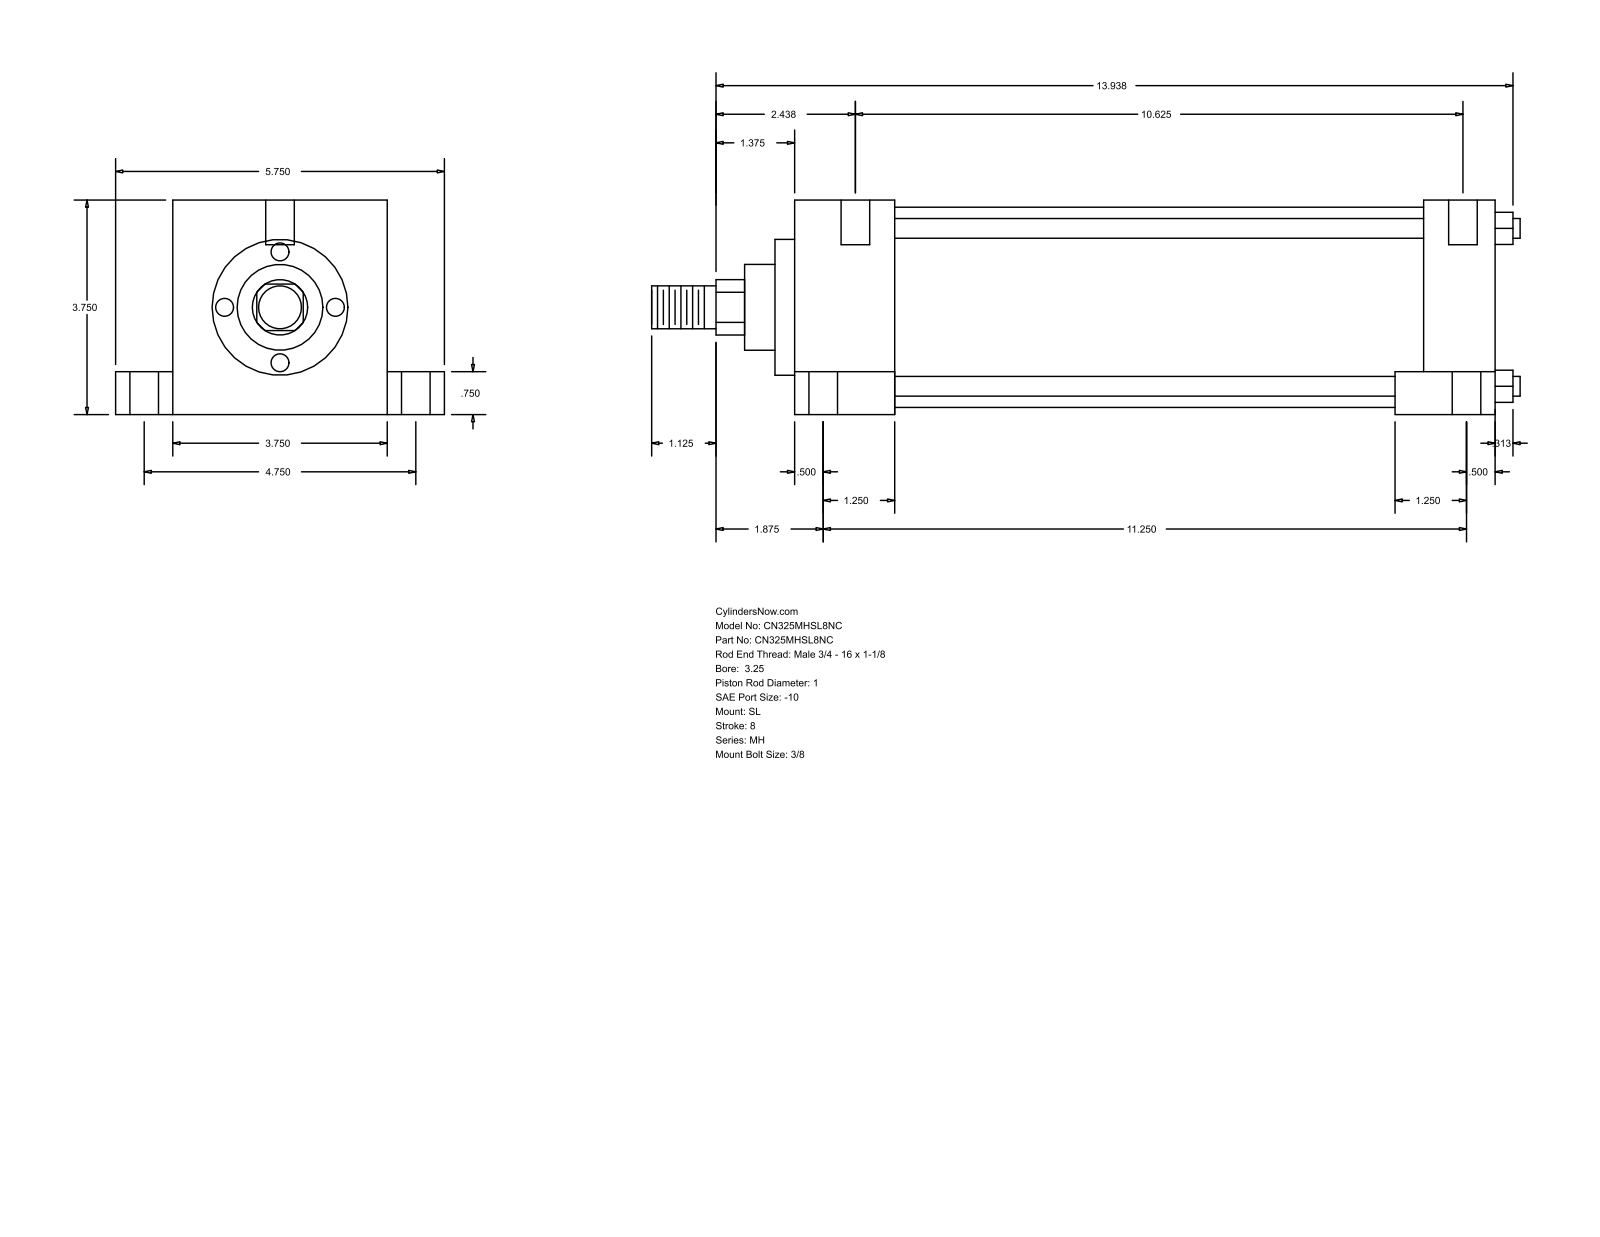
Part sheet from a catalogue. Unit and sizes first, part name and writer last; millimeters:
Units: millimetres
Overall size (bounding box): 385.76 × 146.05 × 95.25
Round holes (diameter × count): ⌀12.7 ×6, ⌀5.56 ×4, ⌀19.05 ×4
Round bosses / shafts (diameter × count): ⌀8.76 ×4, ⌀88.9 ×1, ⌀60.33 ×1, ⌀38.1 ×1, ⌀25.4 ×1, ⌀19.05 ×1
Partial cylindrical surfaces — rounded edges, fillets, slot ends (radius × count): R12.29 ×1
Main face-to-face distances: 95.24, 311.15, 44.46, 266.69, 25.41, 120.65, 19.05, 76.19, 279.4, 234.94
Hole centre spacings: 60.35, 60.41, 61.65, 62, 120.66, 276.22, 278.09, 279.64
Bodies: 0 solids, 110 faces (77 planar, 33 cylindrical, 0 other)
Part name (STEP PRODUCT): MH_SL__0325_1
STEP written by: GSSL Pune (CONFIG_CONTROL_DESIGN)
